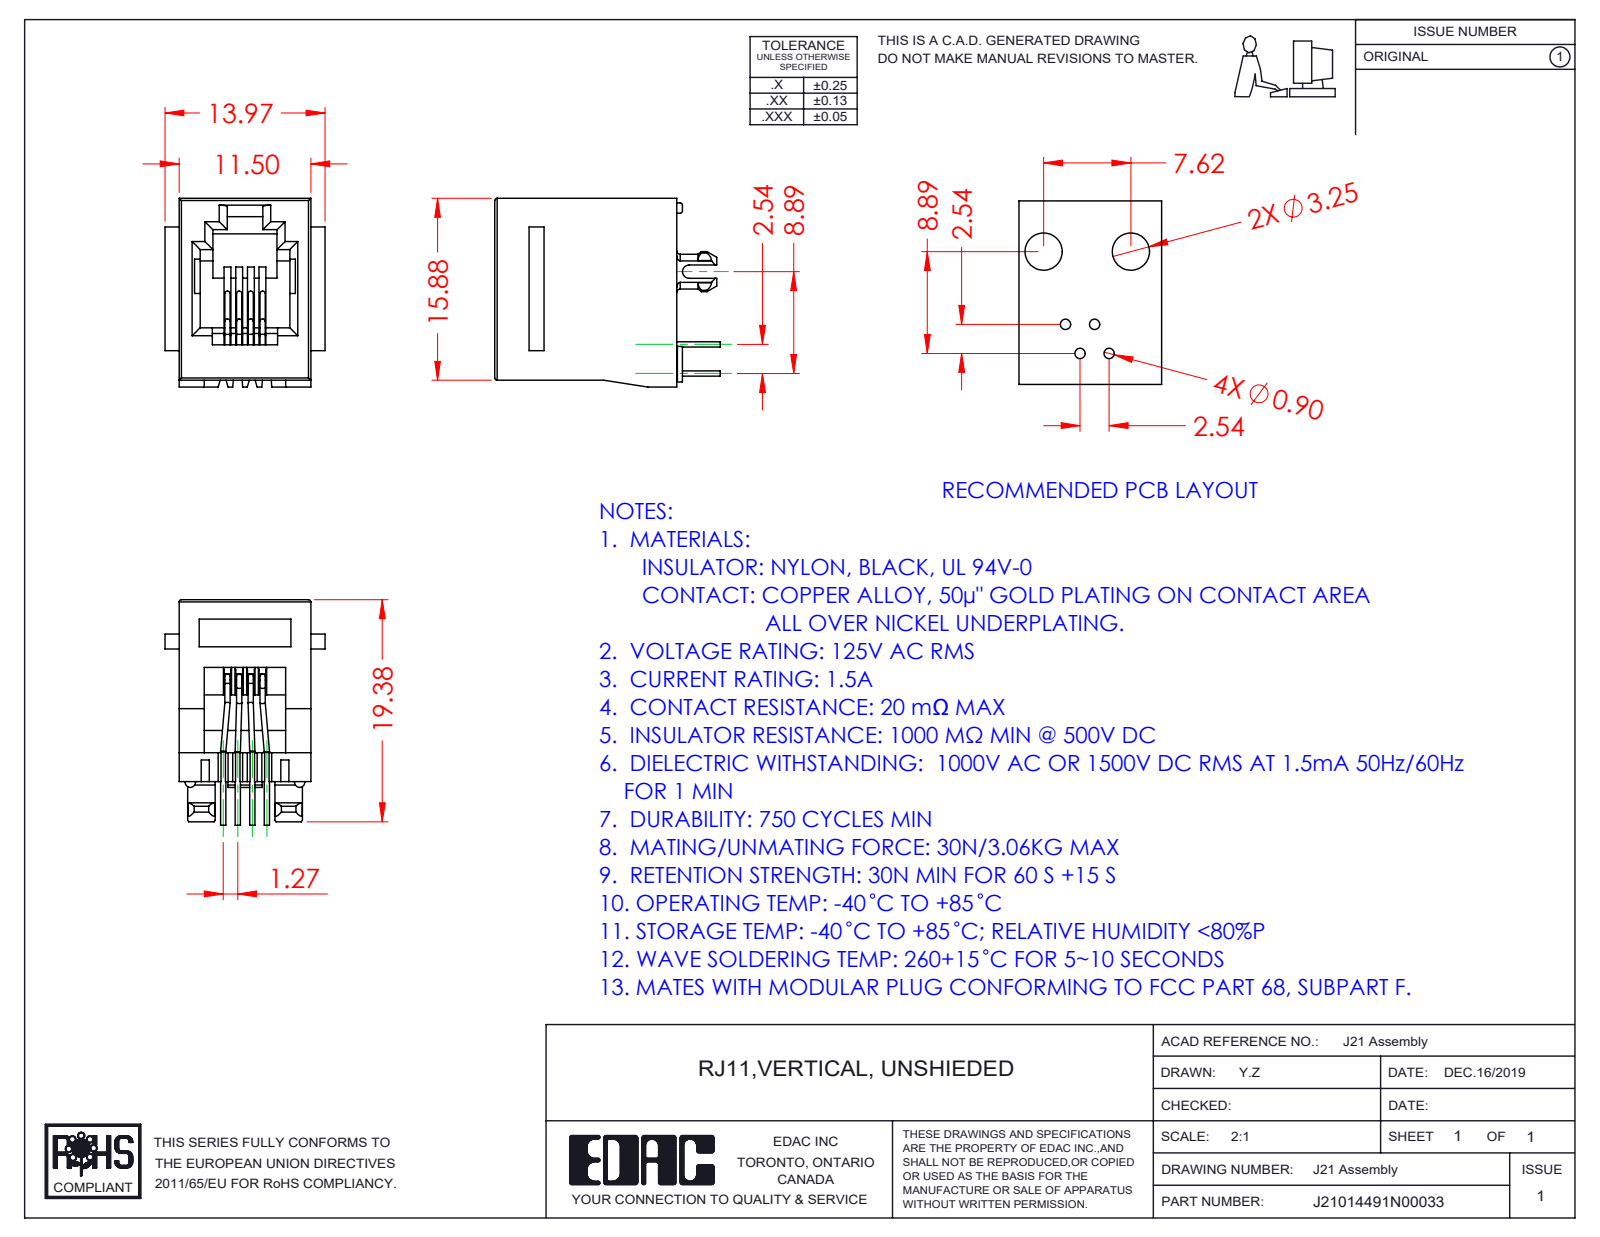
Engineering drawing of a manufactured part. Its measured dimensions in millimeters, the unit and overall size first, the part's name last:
Units: millimetres
Overall size (bounding box): 19.68 × 16.48 × 13.97
Round holes (diameter × count): ⌀2 ×2
Round bosses / shafts (diameter × count): ⌀0.46 ×24
Partial cylindrical surfaces — rounded edges, fillets, slot ends (radius × count): R0.5 ×9, R0.7 ×9, R0.2 ×7, R0.23 ×4, R0.45 ×2, R1.52 ×2, R1.75 ×2, R0.57 ×1
Main face-to-face distances: 11.5, 1.6, 15.88, 1.02, 7.2, 0.6, 2.95, 8.55, 2.04, 1.35
Hole centre spacings: 8.4
Volume: 1 616 mm³ · Surface area: 2 564 mm²
Bodies: 5 solids, 369 faces (230 planar, 111 cylindrical, 28 other)
Part name (STEP PRODUCT): RJ21014491N00033; 21 Contacts; 21 Insulator
STEP written by: SolidWorks 2016 (CONFIG_CONTROL_DESIGN)
